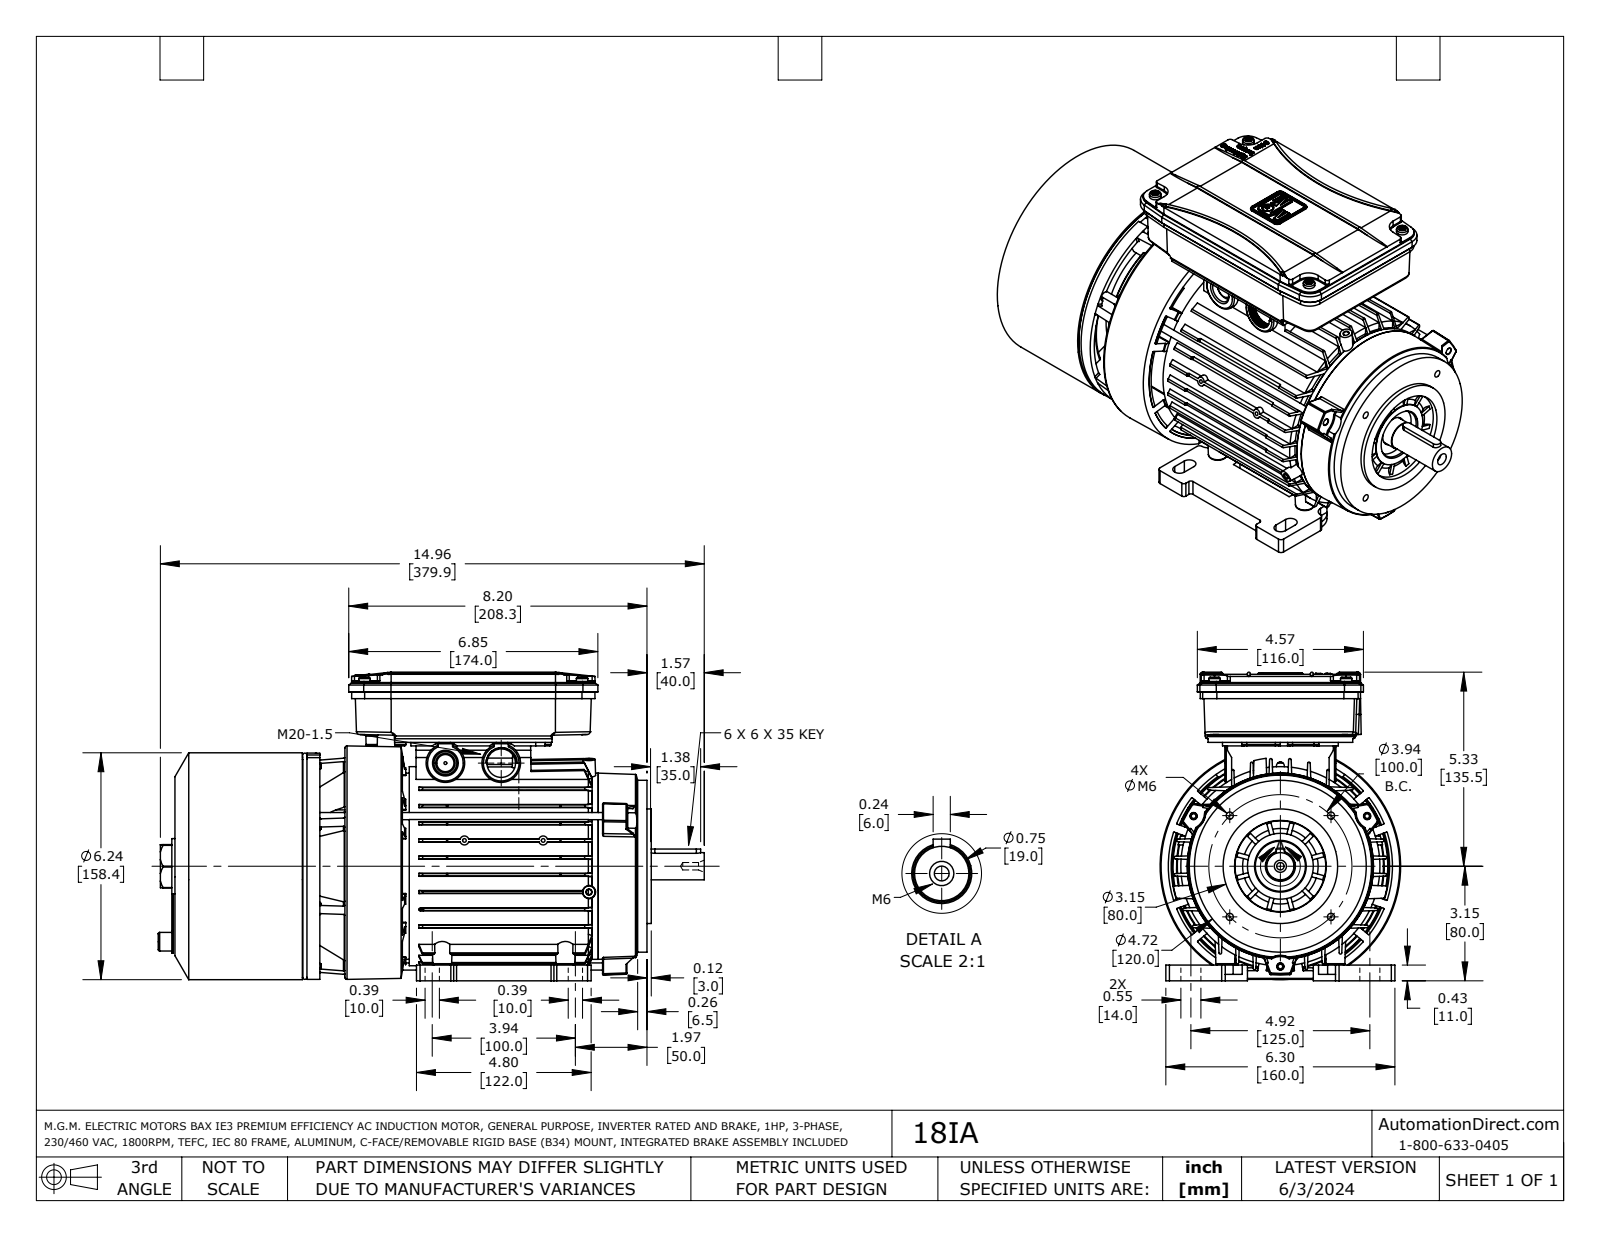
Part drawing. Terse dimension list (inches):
name: 18IA
written by: SolidWorks 2021 (AUTOMOTIVE_DESIGN)
unit: in
bodies: 17 solids, 3847 faces (1378 planar, 1206 cylindrical, 1263 other)
size: 15.015 × 8.484 × 6.614
volume: 105.5 in³; area: 1 182 in²
holes: 14× ⌀0.13, 8× ⌀0.146, 8× ⌀0.236, 7× ⌀0.098, 7× ⌀0.197, 7× ⌀0.217, 4× ⌀0.118, 4× ⌀0.157, 4× ⌀0.177, 4× ⌀0.394, 3× ⌀0.181, 3× ⌀0.276
bosses: 8× ⌀0.177, 8× ⌀0.118, 4× ⌀0.386, 4× ⌀0.315, 4× ⌀0.197, 4× ⌀0.157, 3× ⌀0.256, 3× ⌀0.236
rounds: 74× R0.039, 56× R0.008, 56× R0.02, 35× R0.079, 30× R0.035, 24× R0.012, 16× R0.004, 16× R0.087
face distances: 7.992, 0.433, 0.079, 8.425, 0.047, 0.236, 0.078, 1.493, 1.571, 0.197
hole spacings: 0.472, 0.819, 0.473, 1.222, 1.576, 1.681, 1.969, 2.773
